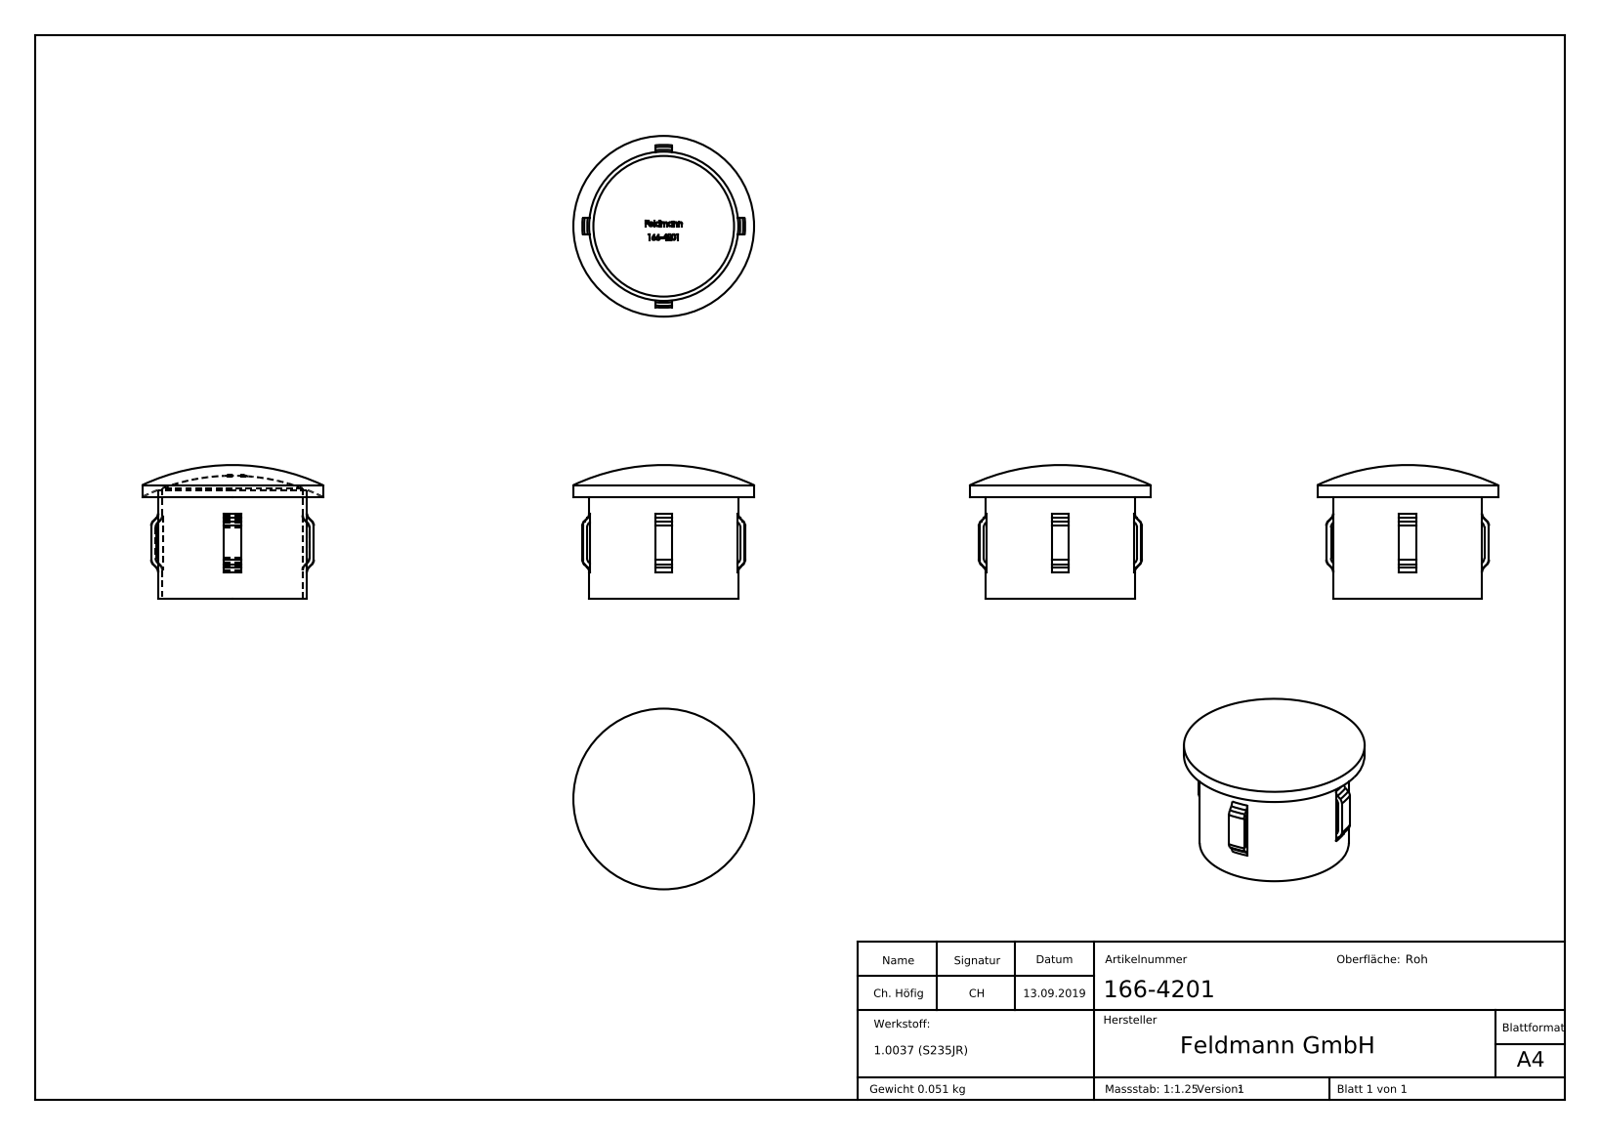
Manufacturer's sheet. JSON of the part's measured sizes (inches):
{"part_name": "166-4201", "step_written_by": "SolidWorks 2015 (CONFIG_CONTROL_DESIGN)", "units": "inches", "bodies": {"solids": 1, "faces": 307, "planar": 112, "cylindrical": 16, "other": 179}, "overall_size": [1.669, 1.669, 1.236], "volume_in3": 0.396, "surface_area_in2": 14.04, "round_holes": [[1.299, 1]], "round_bosses_or_shafts": [[1.669, 1], [1.378, 1]], "partial_cylinders_radius": [[0.713, 1], [0.752, 1]], "face_to_face_distances": [0.157, 0.079, 0.153, 0.05, 0.265, 0.056, 0.117, 0.144, 0.129, 0.112]}
